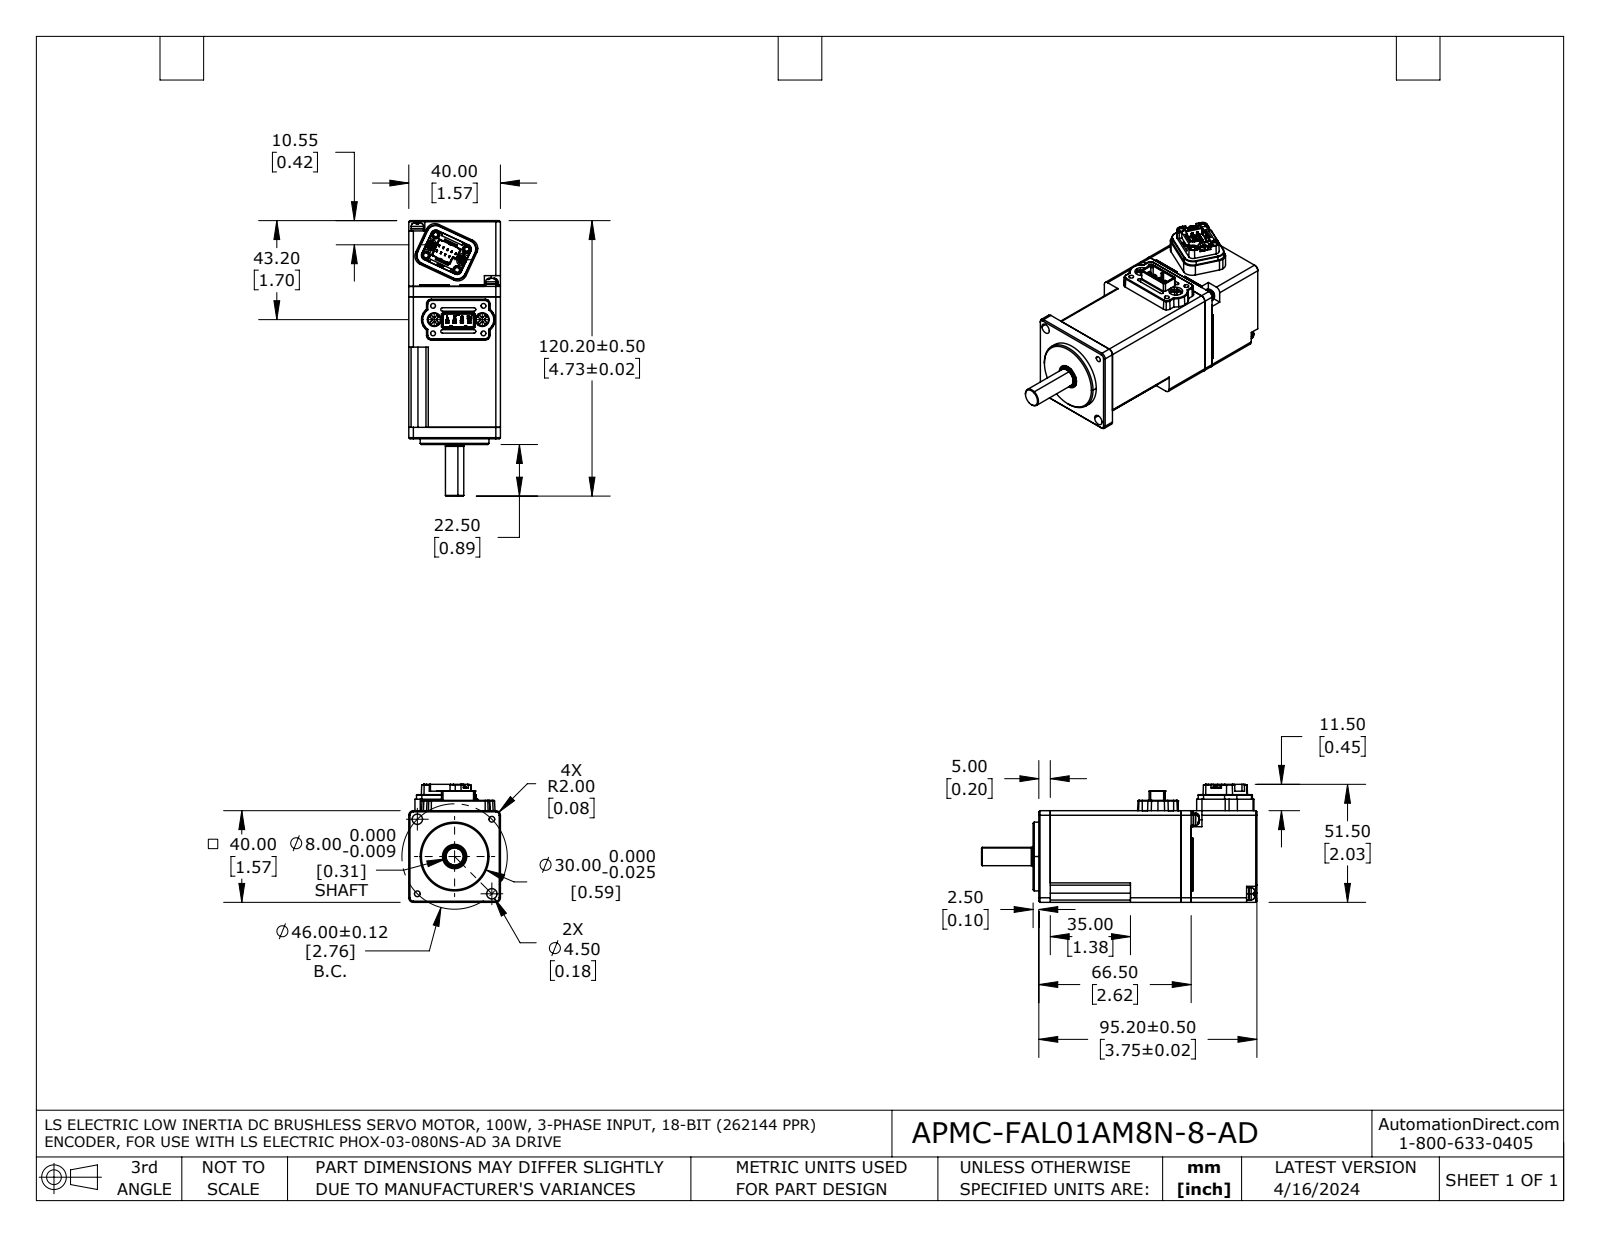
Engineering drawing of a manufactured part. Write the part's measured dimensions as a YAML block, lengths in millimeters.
part_name: "APMC-FAL01AM8N-8-AD"
step_written_by: "SolidWorks 2021 (AUTOMOTIVE_DESIGN)"
units: millimeters
bodies: {solids: 28, faces: 1444, planar: 911, cylindrical: 355, other: 178}
overall_size: [120.2, 51.5, 40]
volume: 155400
surface_area: 42630
round_holes:
  - {diameter: 2.1, count: 10}
  - {diameter: 3, count: 6}
  - {diameter: 3.6, count: 4}
  - {diameter: 2, count: 2}
  - {diameter: 2.5, count: 2}
  - {diameter: 4.5, count: 2}
  - {diameter: 6, count: 2}
  - {diameter: 3.3, count: 1}
  - {diameter: 3.4, count: 1}
  - {diameter: 10.6, count: 1}
round_bosses_or_shafts:
  - {diameter: 5.4, count: 6}
  - {diameter: 2.2, count: 2}
  - {diameter: 30, count: 1}
  - {diameter: 9.8, count: 1}
  - {diameter: 8, count: 1}
partial_cylinders:
  - {radius: 0.2, count: 20}
  - {radius: 0.2, count: 9}
  - {radius: 1, count: 8}
  - {radius: 0.5, count: 7}
  - {radius: 0.1, count: 6}
  - {radius: 1.5, count: 6}
  - {radius: 0.3, count: 4}
  - {radius: 0.8, count: 4}
face_to_face_distances: [40, 4.5, 61.5, 57, 0.7, 5.2, 62.2, 5, 28.7, 2.5]
hole_center_spacings: [6, 16, 22.3, 23, 32.5, 5, 5, 10]
